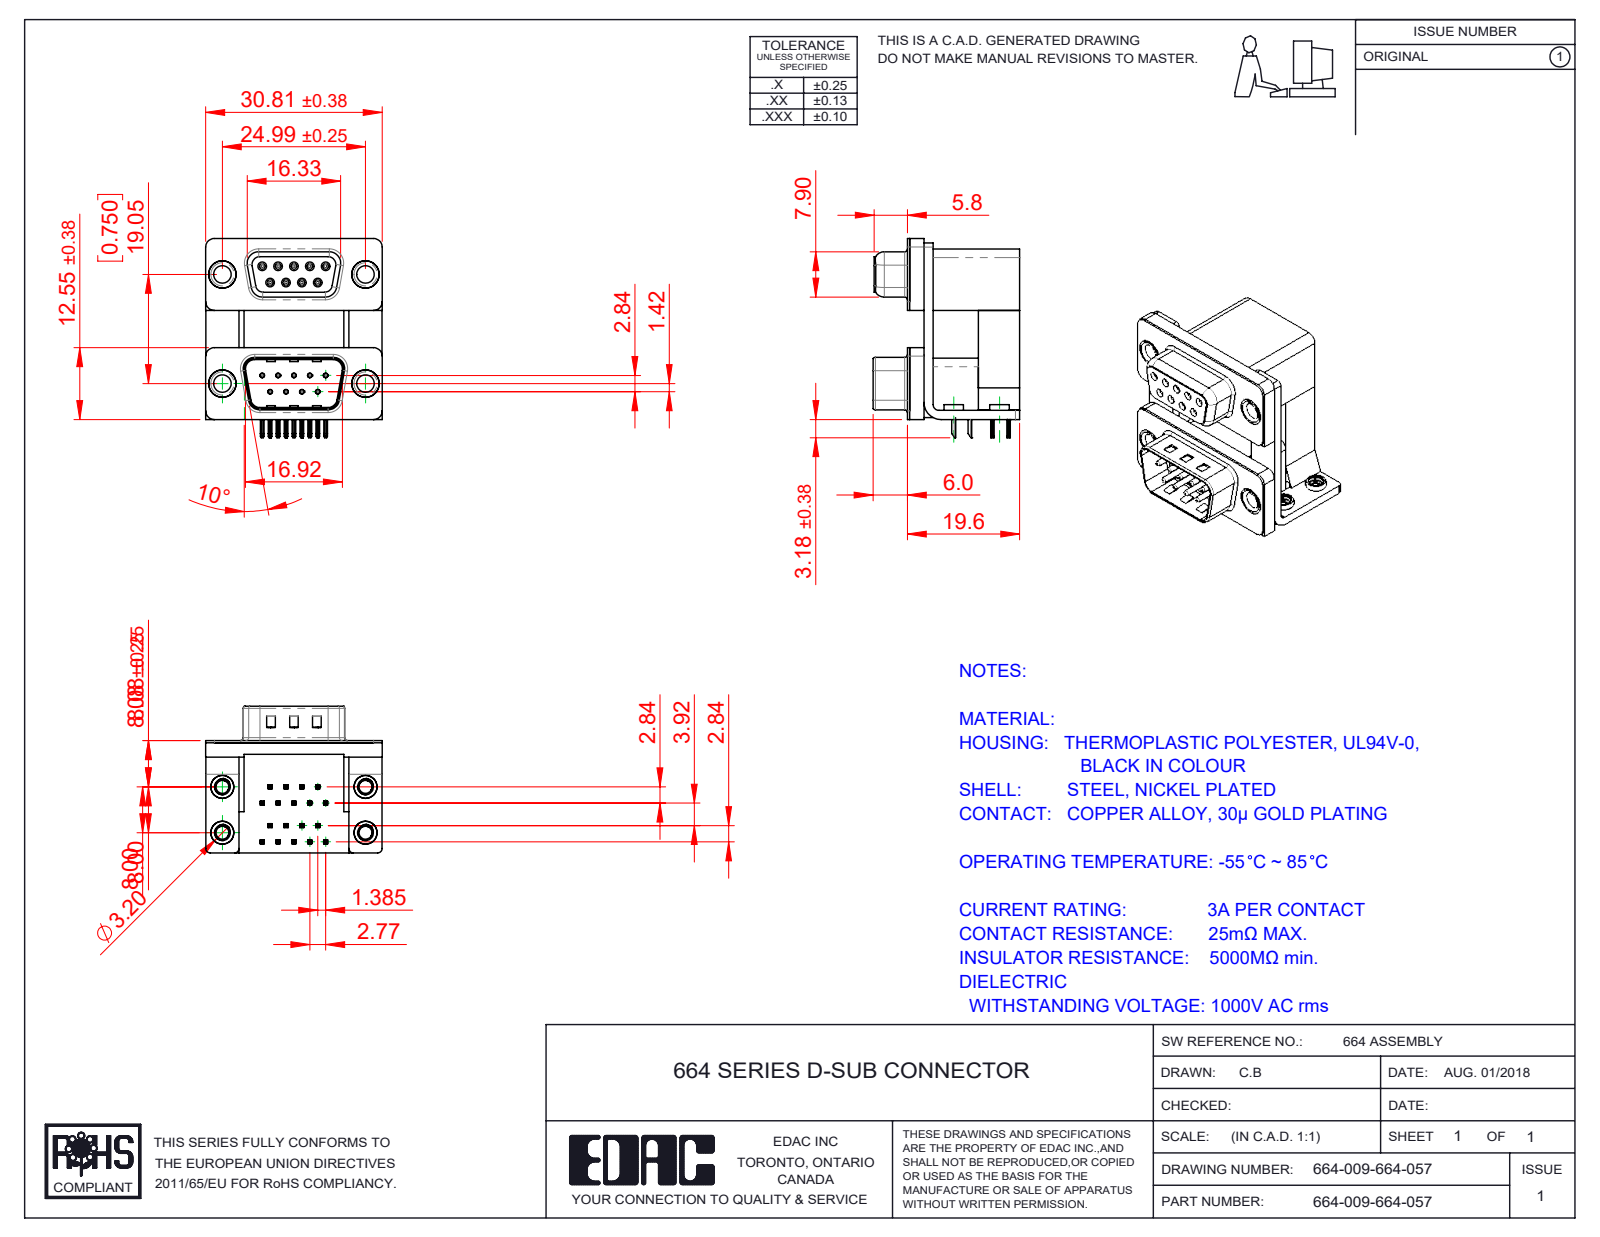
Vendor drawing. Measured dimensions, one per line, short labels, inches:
name: 664 Thru Hole Rivet; 664 Housing Lower_09 Contacts; 664 Contact Bottom Upper_M; 664 Mounting Bracket_ThruM (+8 more)
written by: SolidWorks 2020 (CONFIG_CONTROL_DESIGN)
unit: in
bodies: 33 solids, 2585 faces (1275 planar, 735 cylindrical, 575 other)
size: 1.369 × 1.213 × 1.008
volume: 0.658 in³; area: 19.77 in²
holes: 18× ⌀0.031, 9× ⌀0.014, 9× ⌀0.035, 4× ⌀0.089, 4× ⌀0.108, 4× ⌀0.12, 4× ⌀0.126, 4× ⌀0.138, 4× ⌀0.157, 4× ⌀0.189, 4× ⌀0.197
bosses: 9× ⌀0.047, 9× ⌀0.03, 4× ⌀0.193, 4× ⌀0.187, 4× ⌀0.157, 4× ⌀0.152, 4× ⌀0.134
rounds: 72× R0.004, 36× R0.006, 36× R0.01, 18× R0.005, 18× R0.014, 13× R0.059, 12× R0.02, 9× R0.013
face distances: 0.016, 0.098, 0.657, 0.756, 0.283, 0.374, 0.472, 0.063, 0.772, 0.488
hole spacings: 0.124, 0.109, 0.758, 0.75, 0.218, 0.781, 0.641, 0.863
